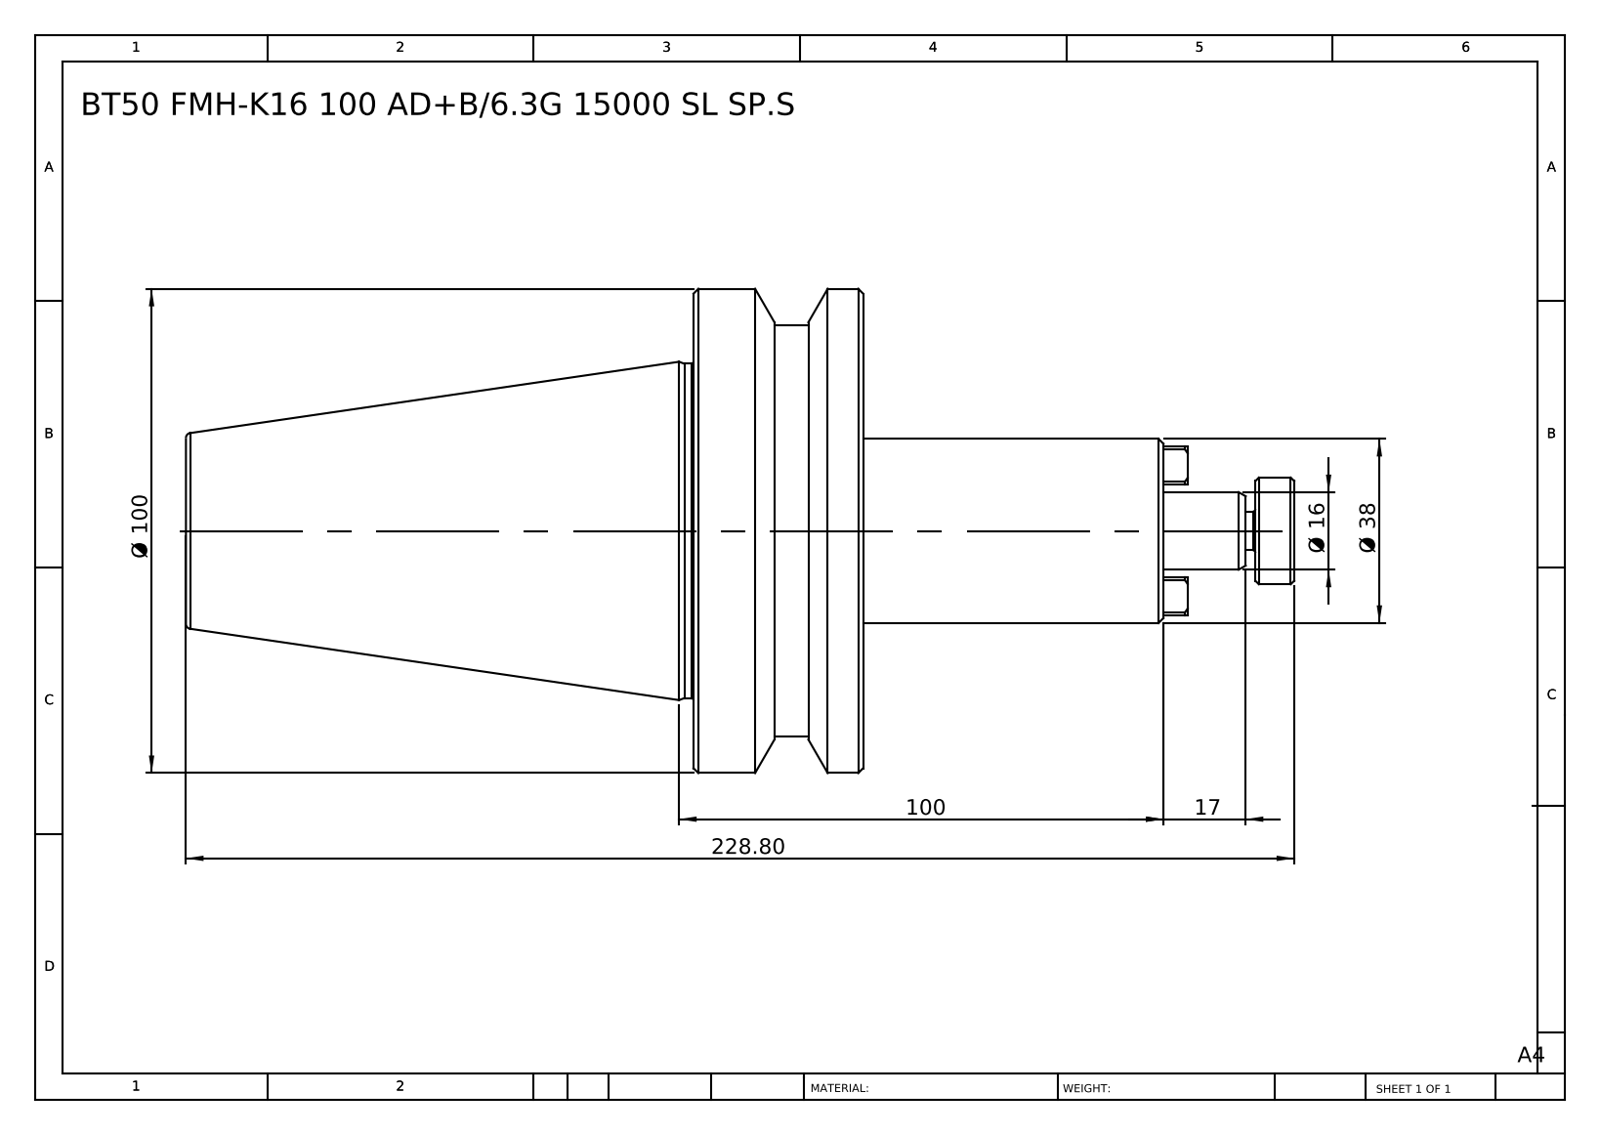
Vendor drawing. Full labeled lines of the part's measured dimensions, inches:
Part name (STEP PRODUCT): BT50 FMH16 100 AD-6.3G 15000 SL SP.S
STEP written by: SolidWorks 2014 (CONFIG_CONTROL_DESIGN)
Units: inches
Bodies: 1 solid, 77 faces (35 planar, 16 cylindrical, 26 other)
Overall size (bounding box): 9.008 × 3.937 × 3.937
Volume: 35.85 in³ · Surface area: 83.73 in²
Round bosses / shafts (diameter × count): ⌀3.937 ×1, ⌀3.346 ×1, ⌀2.717 ×1, ⌀1.496 ×1, ⌀0.866 ×1, ⌀0.63 ×1, ⌀0.315 ×1
Main face-to-face distances: 1.378, 5.504, 4.126, 2.441, 3.819, 7.945, 0.315, 1.063, 3.504, 4.882
